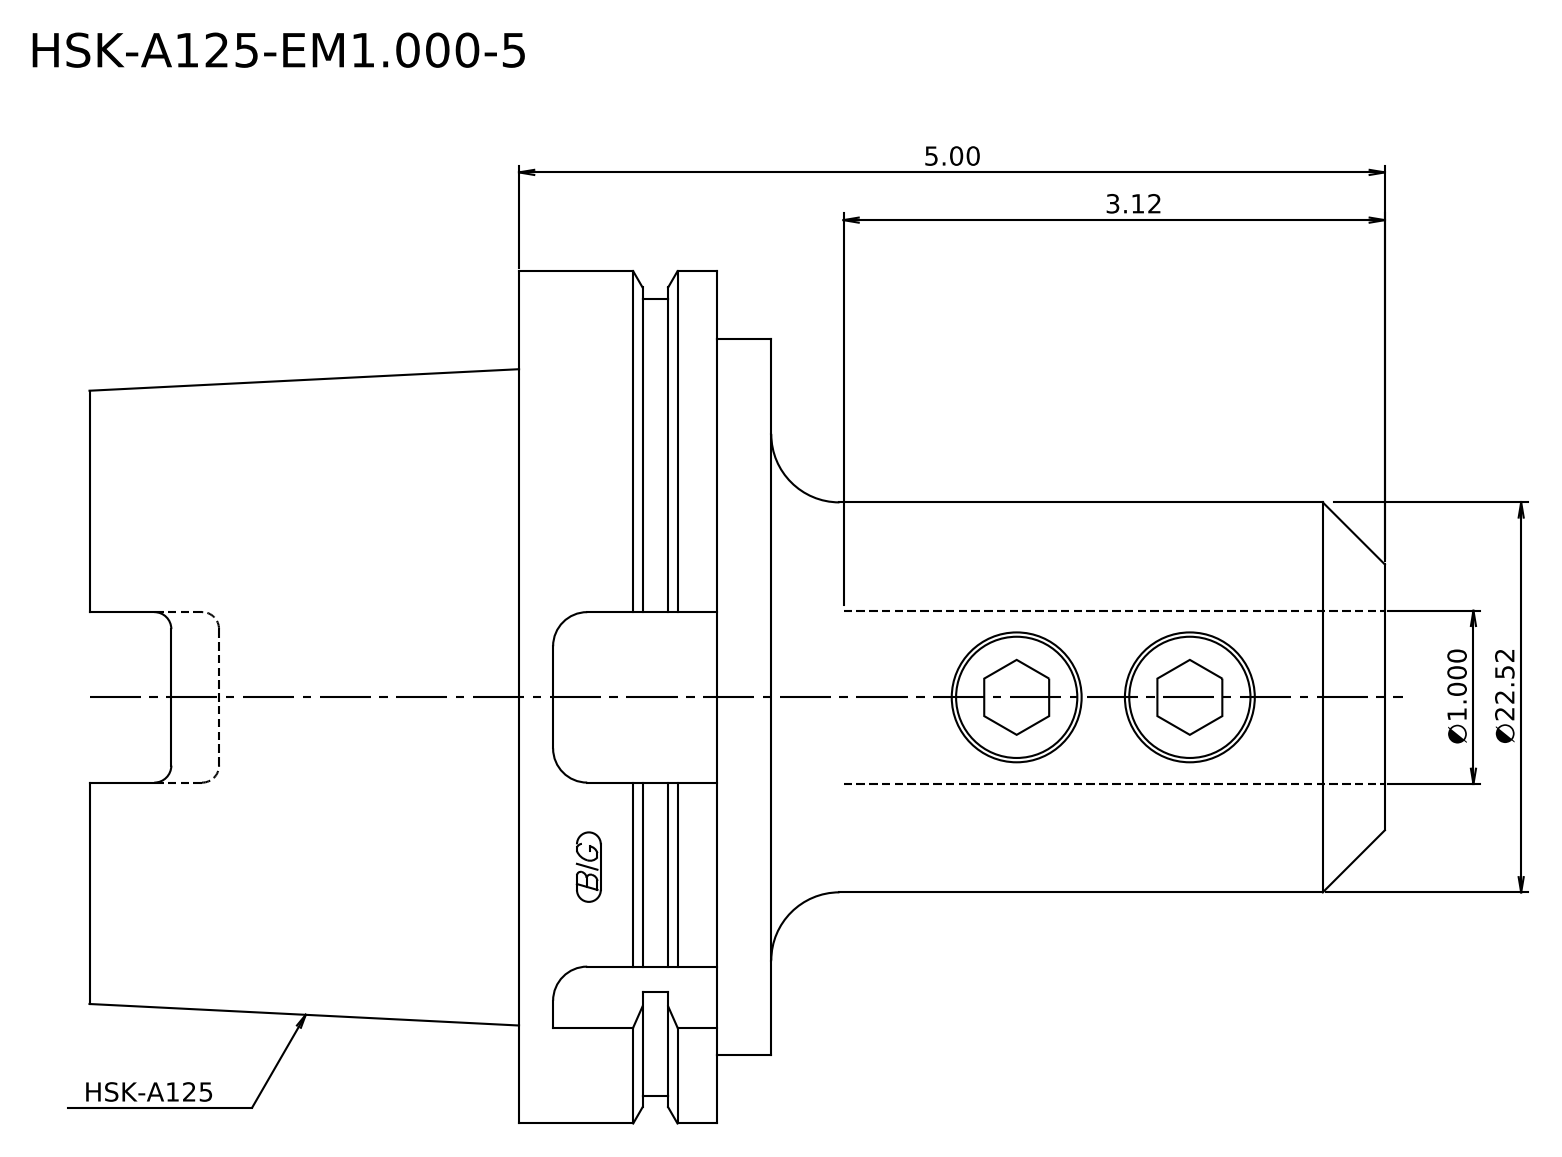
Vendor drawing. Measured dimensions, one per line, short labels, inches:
written by: Kubotek KeyCreator 2011 V10.0.2 (22737) (automotive_design)
unit: in
bodies: 1 solid, 17 faces (7 planar, 5 cylindrical, 5 other)
size: 7.48 × 4.921 × 4.921
volume: 66.03 in³; area: 112.3 in²
bosses: 1× ⌀4.921, 1× ⌀4.606, 1× ⌀4.134, 1× ⌀2.252
face distances: 2.48, 1.457, 3.937, 0.315, 1.142, 3.622, 3.543, 3.858, 5, 7.48
